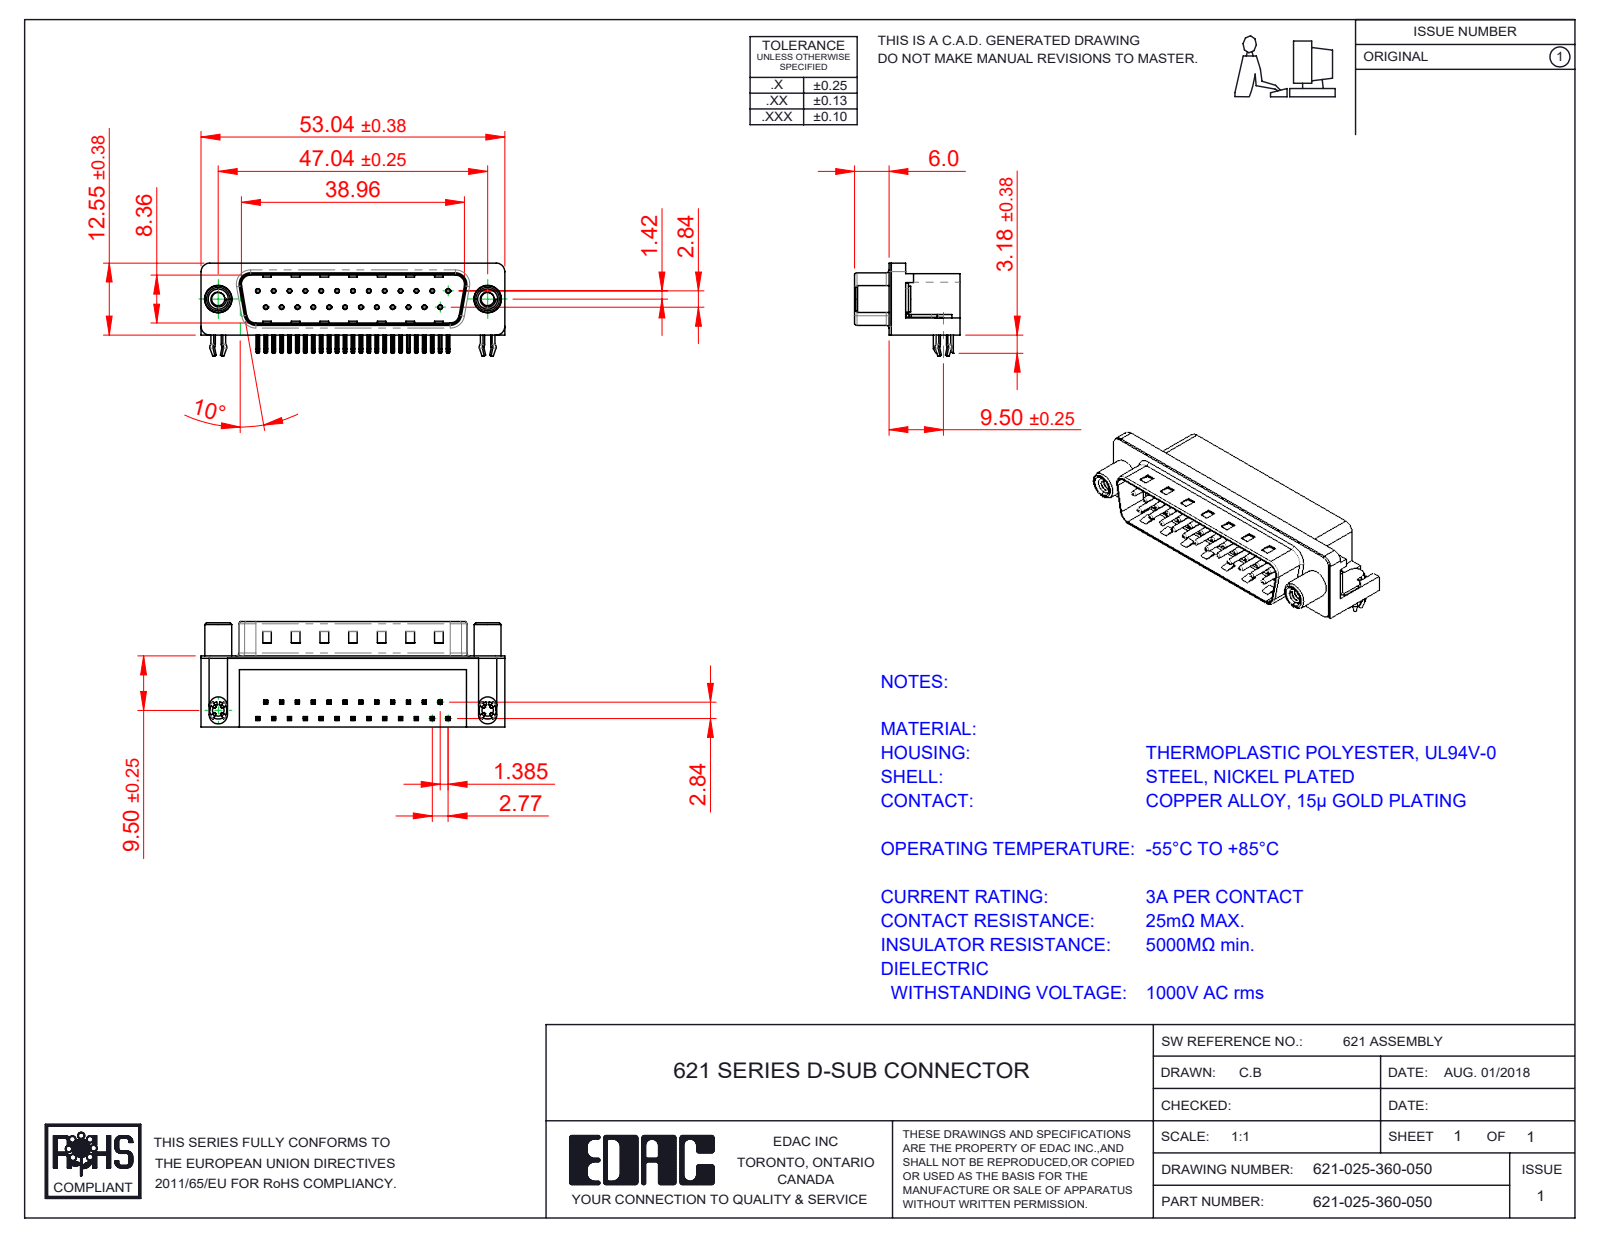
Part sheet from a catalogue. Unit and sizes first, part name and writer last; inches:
Units: inches
Overall size (bounding box): 2.088 × 0.724 × 0.619
Round holes (diameter × count): ⌀0.014 ×25, ⌀0.031 ×25, ⌀0.089 ×2, ⌀0.091 ×2, ⌀0.122 ×2, ⌀0.157 ×2, ⌀0.189 ×2, ⌀0.197 ×2
Round bosses / shafts (diameter × count): ⌀0.03 ×25, ⌀0.193 ×2, ⌀0.185 ×2, ⌀0.177 ×2, ⌀0.152 ×2, ⌀0.128 ×2
Partial cylindrical surfaces — rounded edges, fillets, slot ends (radius × count): R0.01 ×100, R0.005 ×50, R0.039 ×16, R0.02 ×9, R0.063 ×8, R0.059 ×7, R0.035 ×4, R0.079 ×4
Main face-to-face distances: 0.016, 0.472, 0.407, 0.083, 0.345, 0.412, 0.067, 0.428, 0.488, 0.114
Hole centre spacings: 0.124, 0.109, 0.218, 0.327, 0.436, 0.545, 0.654, 0.198
Volume: 0.394 in³ · Surface area: 12.34 in²
Bodies: 31 solids, 2287 faces (1397 planar, 679 cylindrical, 211 other)
Part name (STEP PRODUCT): 621 Contact Bottom; 621 Housing_25 Socket; 621 Round Threaded Standoff; 621 Contact Top (+3 more)
STEP written by: SolidWorks 2016 (CONFIG_CONTROL_DESIGN)
